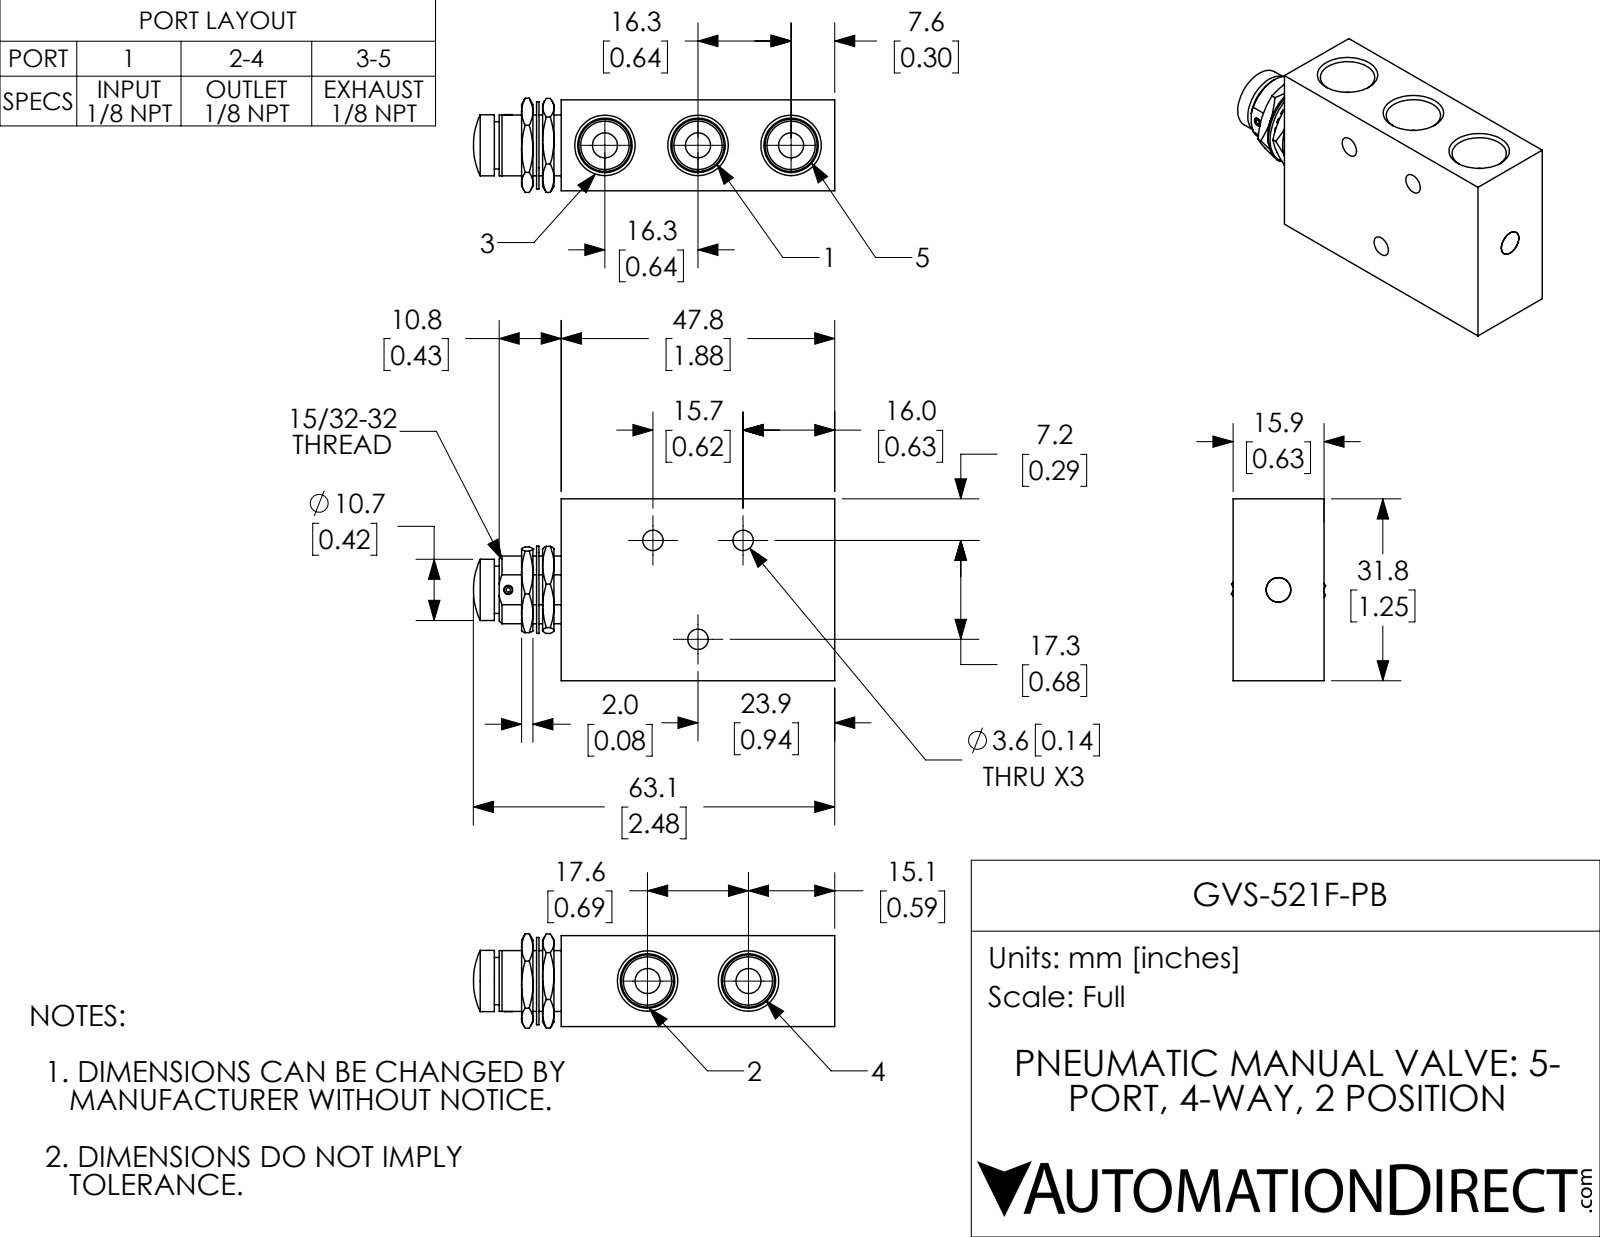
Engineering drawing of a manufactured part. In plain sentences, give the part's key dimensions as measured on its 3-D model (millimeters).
The part is named "GVS-521F-PB". Its 3-D file was written by "SolidWorks 2018 (AUTOMOTIVE_DESIGN)". It is 7 solids with 308 faces: 115 planar, 123 cylindrical and 70 other. Overall it measures 63.1 by 31.8 by 16.5 millimeters. Its volume is 17 700 cubic millimeters and its surface area 11 260 square millimeters. Round holes: 6 of diameter 8.4, 5 of diameter 4.4, 3 of diameter 3.6, 1 of diameter 0.8, 1 of diameter 1.6, 1 of diameter 3.9, 1 of diameter 4.3, 1 of diameter 4.6, 1 of diameter 7.4, 1 of diameter 10.5, 1 of diameter 10.5, 1 of diameter 11.1. Round bosses or shafts: 1 of diameter 15.2, 1 of diameter 10.7, 1 of diameter 8.3, 1 of diameter 1.6. Partial cylindrical surfaces (rounded edges, fillets, slot ends): 2 of radius 0.9, 1 of radius 5.9, 1 of radius 6.1, 1 of radius 6.6. The main face-to-face distances are 15.9, 31.8, 47.8, 1.2, 46.6, 22.9, 8.9, 14, 45.4, 2.6. The hole center spacings are 7.4, 8.8, 16.3, 19, 25.1, 1.1, 15.7, 17.6.
